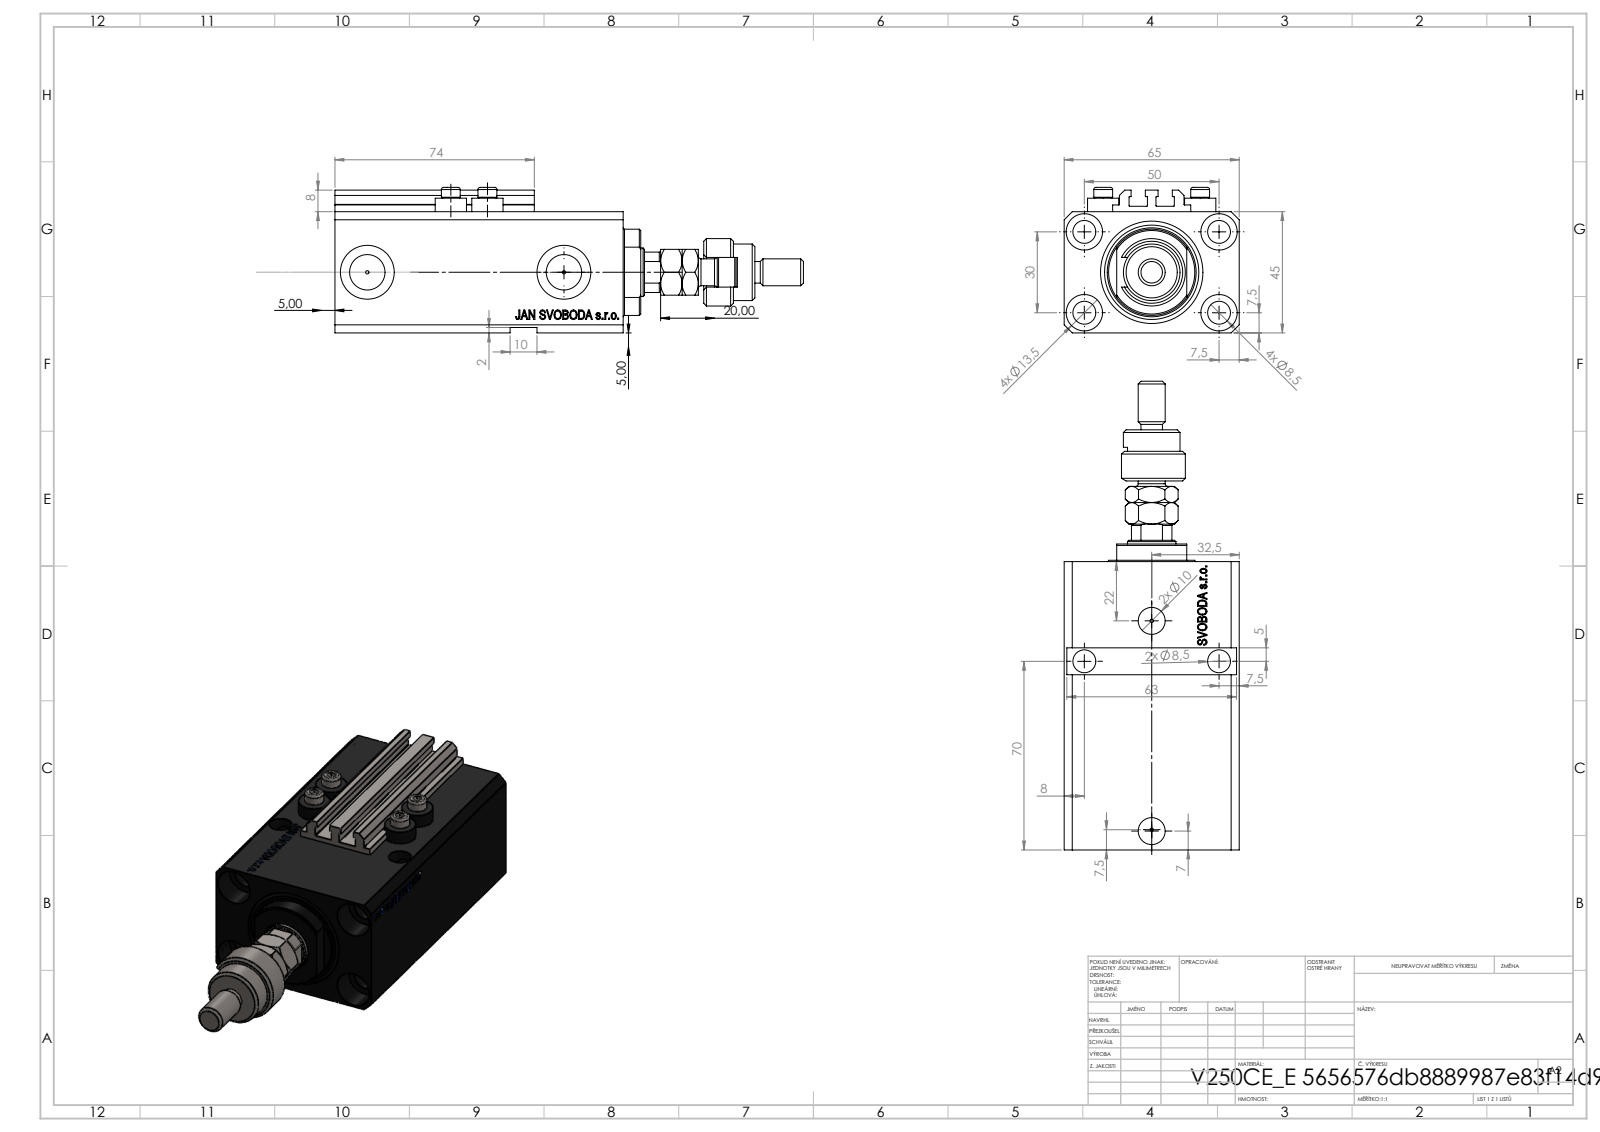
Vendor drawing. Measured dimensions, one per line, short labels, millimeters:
name: FEMALE_PART_FOR_DFA; MFA; V250CE_E_Body; ALLEN BOLT V250CE (+2 more)
written by: SolidWorks 2019 (CONFIG_CONTROL_DESIGN)
unit: mm
bodies: 10 solids, 1172 faces (539 planar, 159 cylindrical, 474 other)
size: 174 × 65 × 54
volume: 285 194 mm³; area: 82 321 mm²
holes: 9× ⌀8.5, 4× ⌀1.25, 4× ⌀4, 4× ⌀13.5, 2× ⌀10, 2× ⌀13.16, 2× ⌀20, 1× ⌀18, 1× ⌀38
bosses: 4× ⌀11.6, 4× ⌀7, 1× ⌀25, 1× ⌀21, 1× ⌀16, 1× ⌀10, 1× ⌀8
rounds: 10× R0.2, 1× R5.5, 1× R8.5, 1× R8.75, 1× R16
face distances: 45, 65, 14, 2, 93, 47, 107, 2.5, 3, 10
hole spacings: 29.15, 50, 13.6, 14.76, 15.12, 27.51, 27.89, 30
